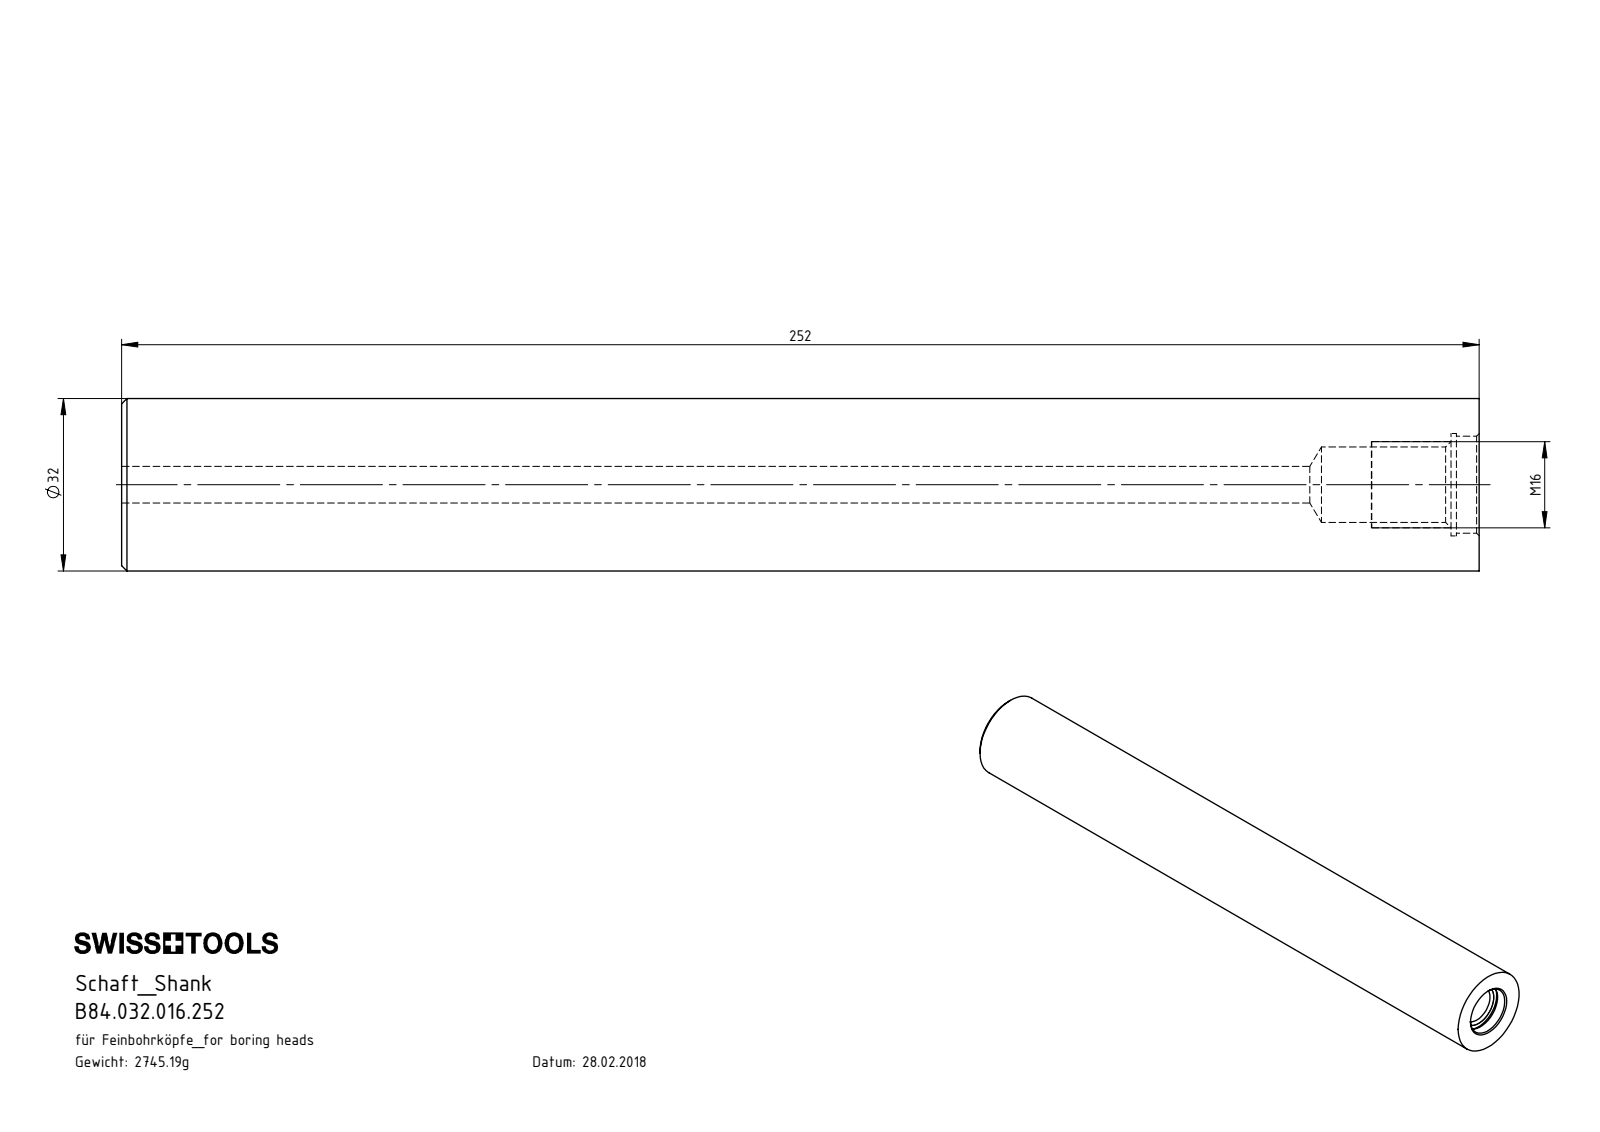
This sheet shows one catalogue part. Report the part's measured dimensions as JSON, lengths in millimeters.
{"part_name": "B84.032.016.252", "step_written_by": "SolidWorks 2017 (CONFIG_CONTROL_DESIGN)", "units": "millimeters", "bodies": {"solids": 1, "faces": 22, "planar": 4, "cylindrical": 10, "other": 8}, "overall_size": [252, 32, 32], "volume_mm3": 189323, "surface_area_mm2": 32916, "round_holes": [[6.8, 1], [14, 1], [18, 1], [19, 1]], "round_bosses_or_shafts": [[32, 1]], "face_to_face_distances": [252, 246.75, 5.25, 247.75, 1, 4.25]}
